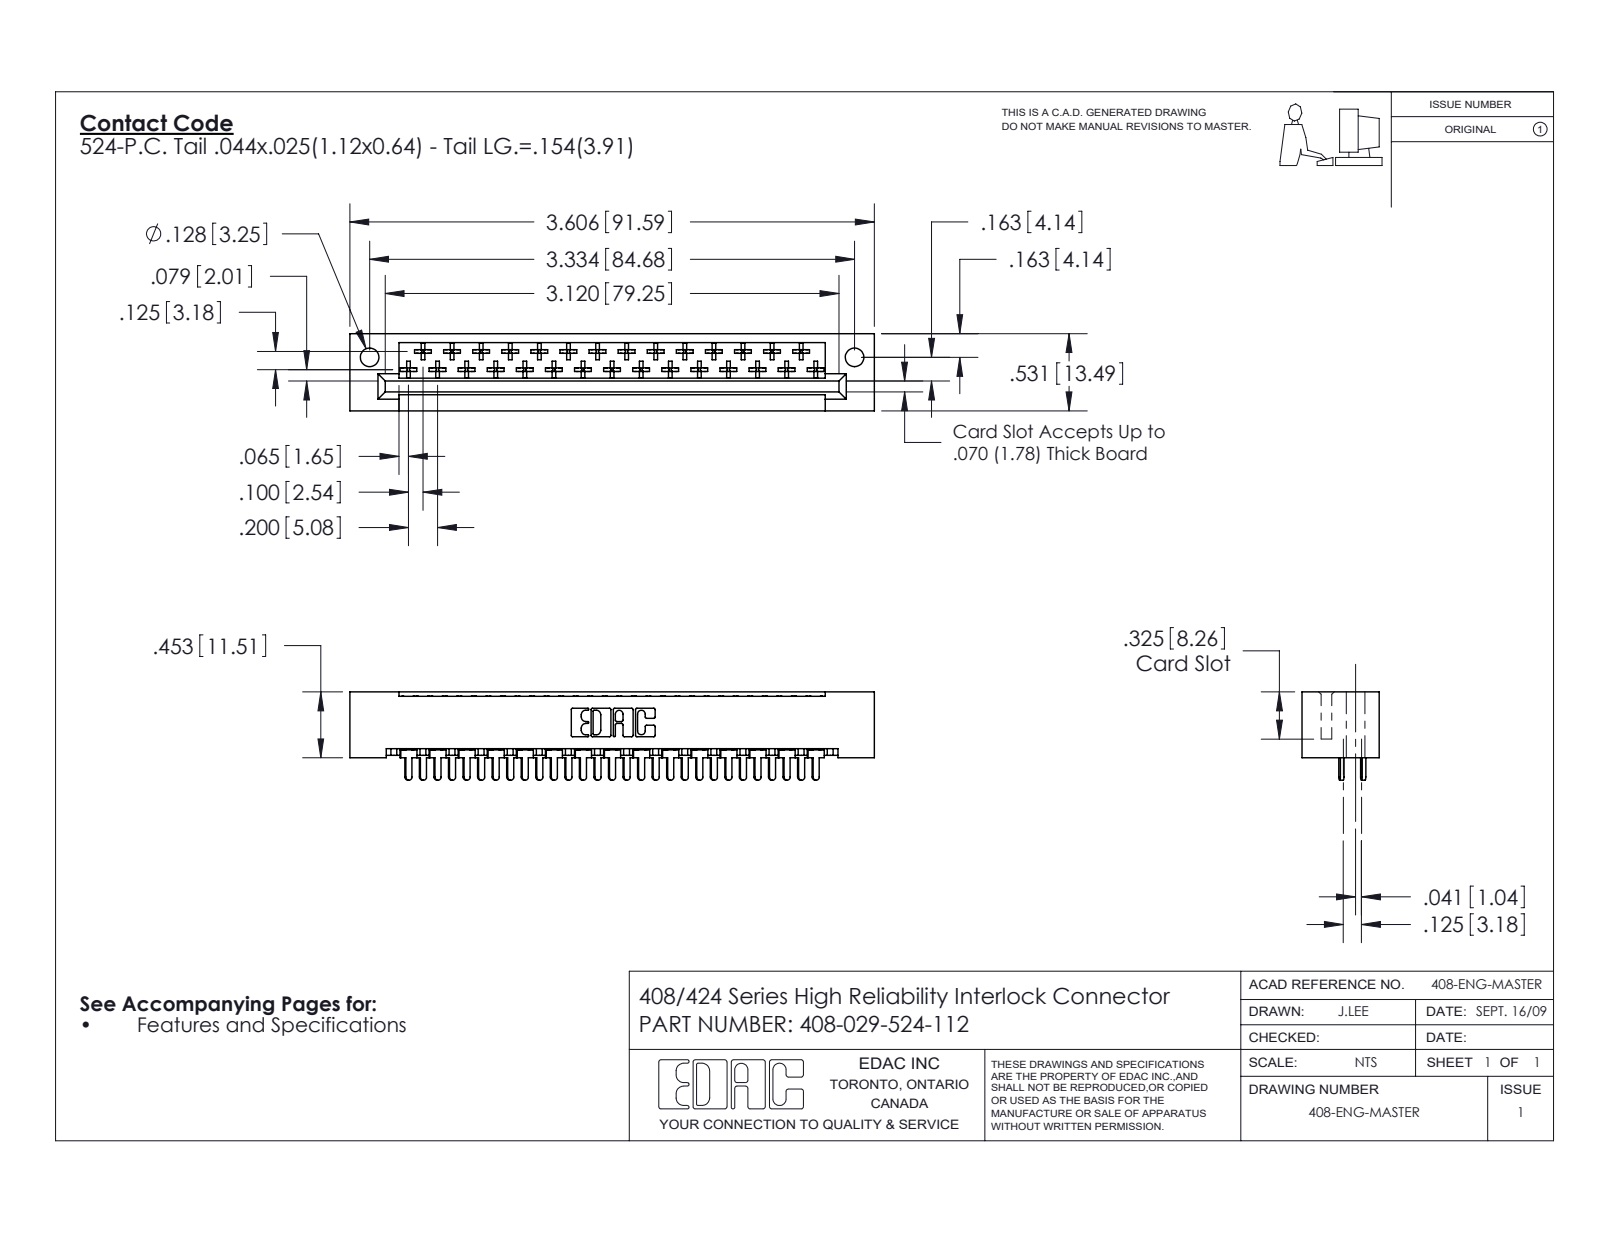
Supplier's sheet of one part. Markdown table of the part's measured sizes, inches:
| quantity | value |
| --- | --- |
| part name | 408 Part_029 - 1; 408-290-001_408-290-124 - Bottom; 408-029-524-112; 408-290-001_408-290-124 - Top |
| STEP written by | SolidWorks 2016 (CONFIG_CONTROL_DESIGN) |
| units | inches |
| bodies | 30 solids, 1725 faces (1297 planar, 312 cylindrical, 116 other) |
| overall size | 3.606 × 0.607 × 0.531 |
| volume | 0.644 in³ |
| surface area | 19.1 in² |
| round holes (diameter × count) | 0.128 × 2 |
| partial cylindrical surfaces (radius × count) | 0.01 × 174, 0.02 × 31, 0.022 × 29, 0.01 × 22, 0.007 × 6, 0.031 × 6, 0.026 × 3 |
| main face-to-face distances | 0.531, 0.025, 0.4, 0.1, 0.125, 0.025, 0.272, 0.235, 0.259, 0.296 |
| hole center spacings | 3.334 |
